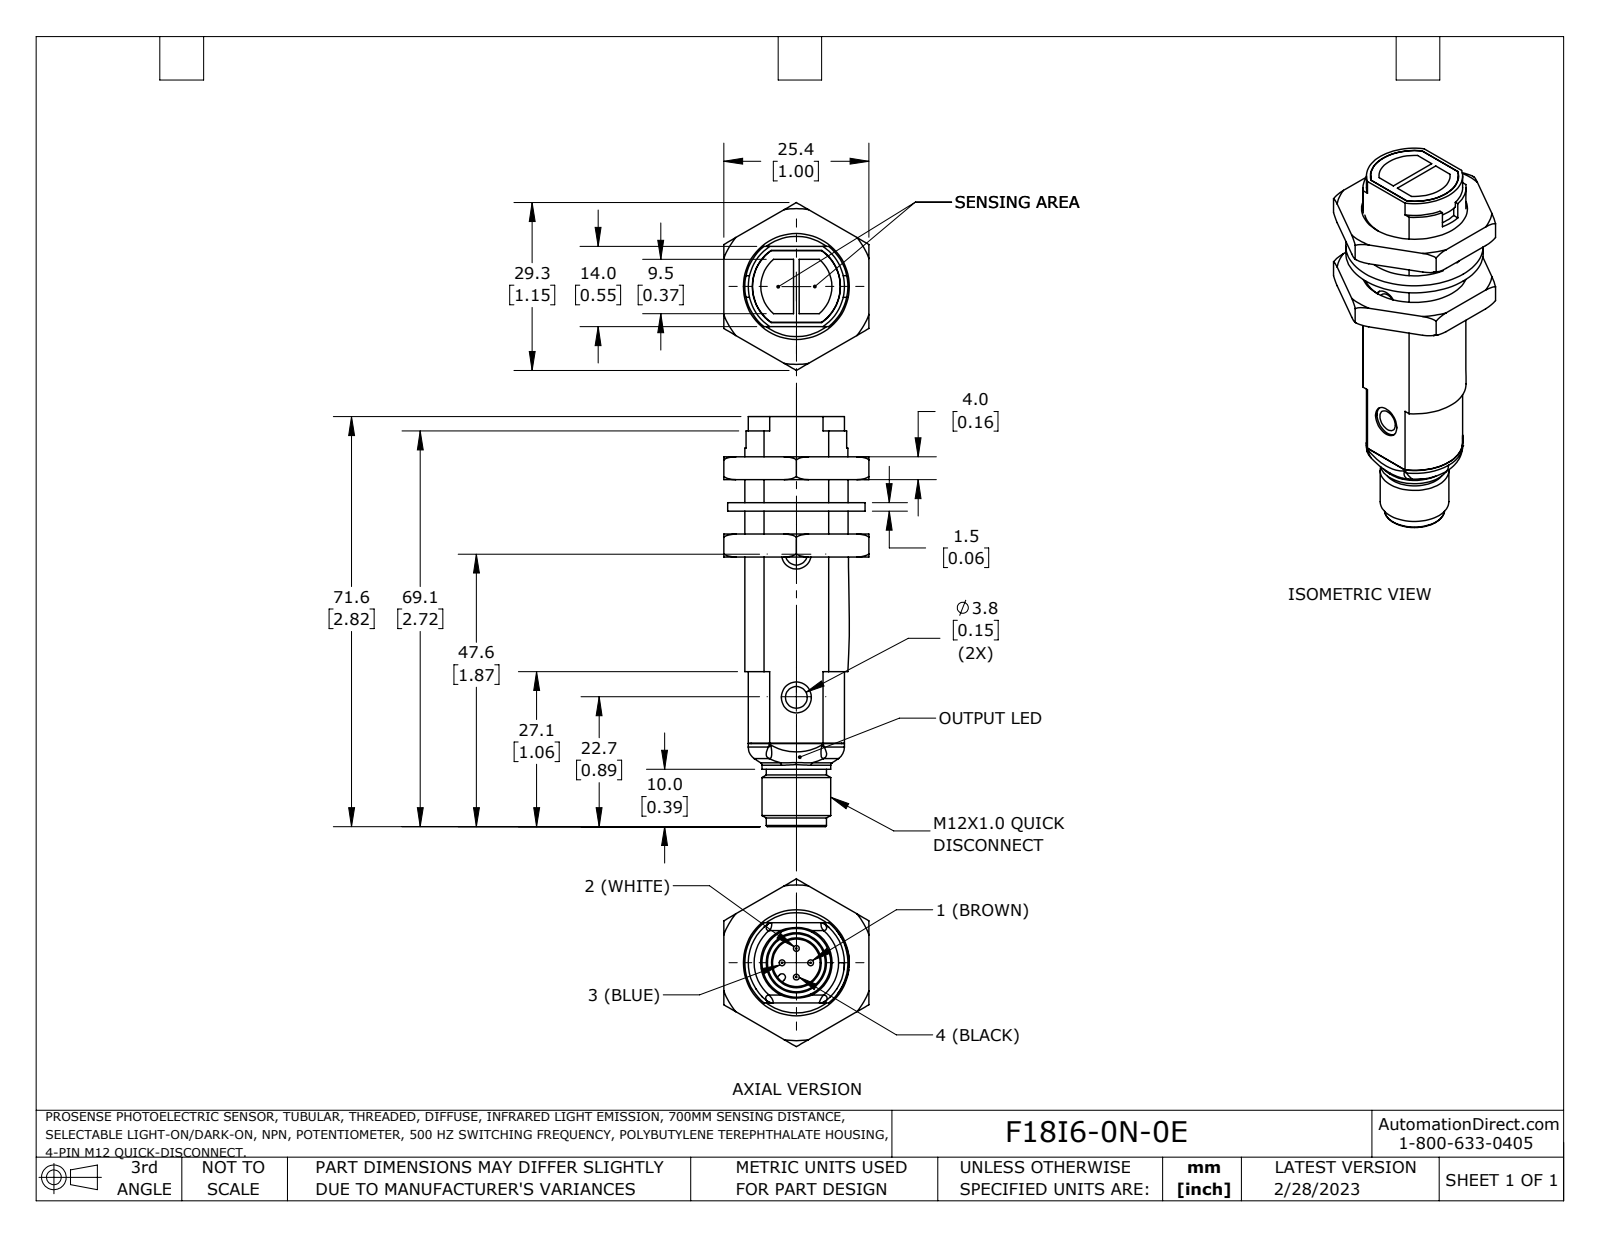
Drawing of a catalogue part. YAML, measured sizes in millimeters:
part_name: "F18I2-0P-0E"
step_written_by: "SolidWorks 2021 (AUTOMOTIVE_DESIGN)"
units: millimeters
bodies: {solids: 4, faces: 178, planar: 72, cylindrical: 46, other: 60}
overall_size: [71.6, 29.3, 25.3]
volume: 16200
surface_area: 7800
round_holes:
  - {diameter: 3.8, count: 2}
  - {diameter: 5.2, count: 1}
  - {diameter: 17.5, count: 1}
  - {diameter: 18, count: 1}
round_bosses_or_shafts:
  - {diameter: 1, count: 4}
  - {diameter: 24, count: 1}
  - {diameter: 12, count: 1}
  - {diameter: 10.5, count: 1}
partial_cylinders:
  - {radius: 1, count: 4}
  - {radius: 1.5, count: 4}
  - {radius: 2.6, count: 2}
  - {radius: 28, count: 2}
  - {radius: 0.6, count: 1}
  - {radius: 7.6, count: 1}
  - {radius: 7.7, count: 1}
  - {radius: 7.9, count: 1}
face_to_face_distances: [4, 9.5, 14, 13.5, 5.5, 8, 25.3, 17.5, 11, 1.5]
hole_center_spacings: [25]
